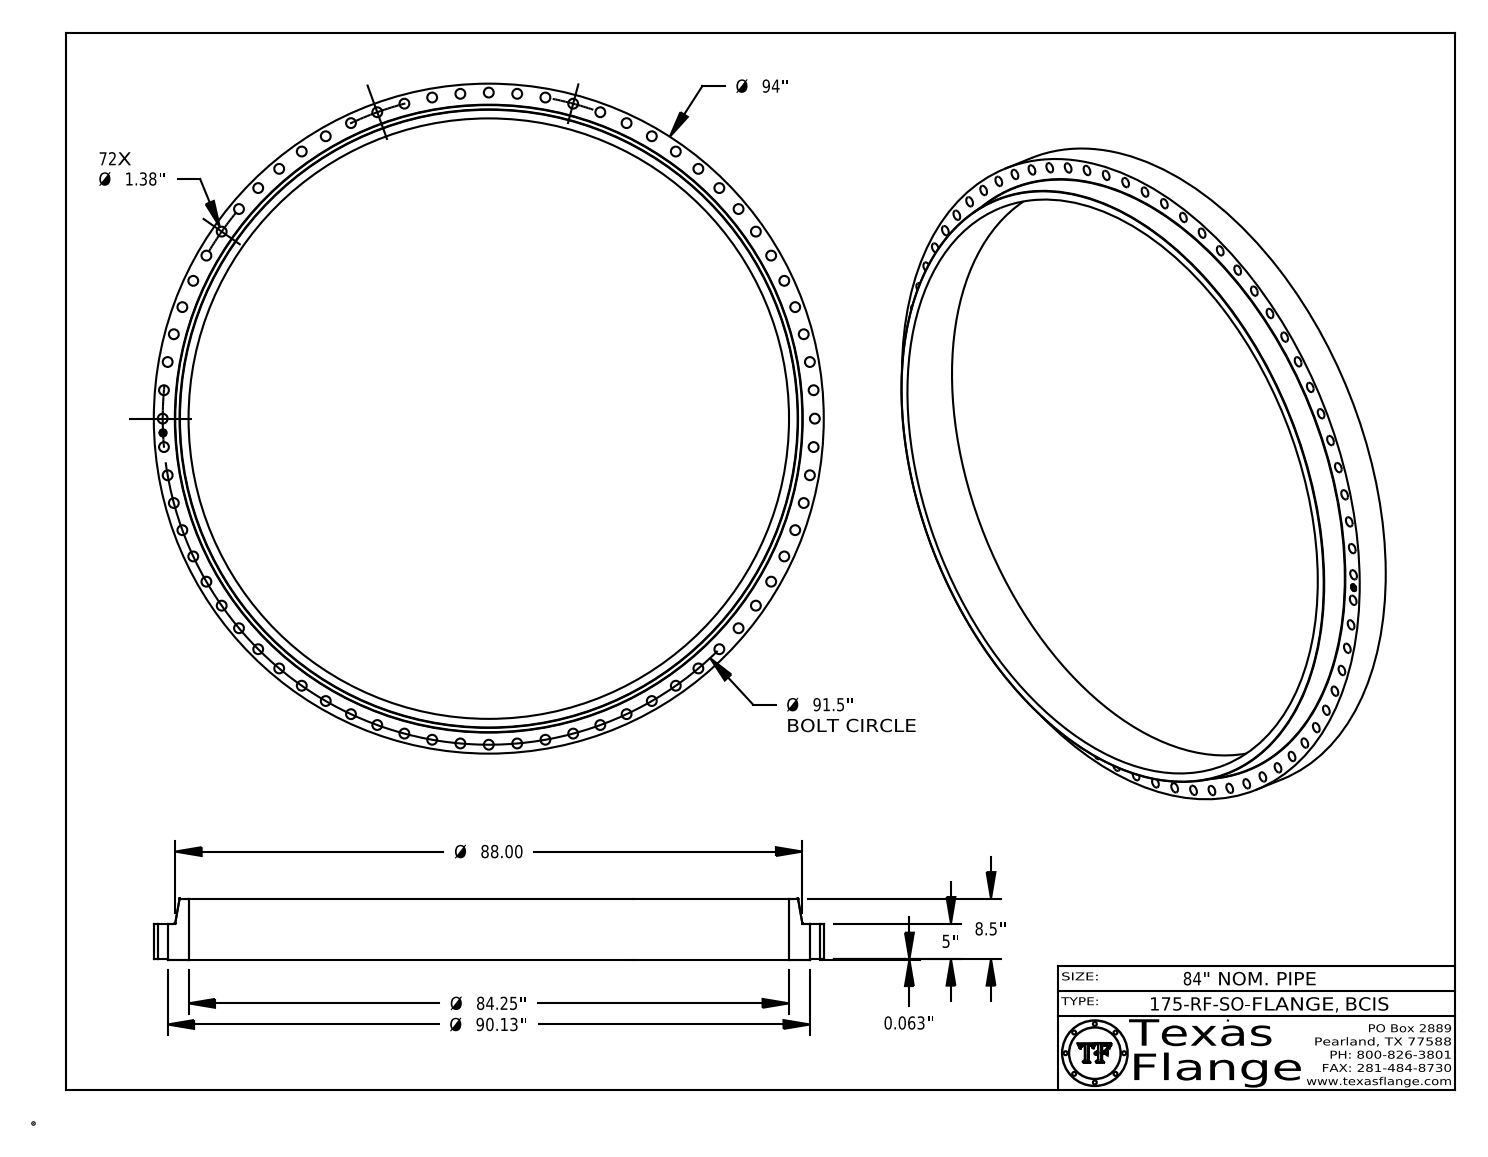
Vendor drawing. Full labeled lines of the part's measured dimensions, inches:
Part name (STEP PRODUCT): 175-RF-SO
STEP written by: CATIA V5 STEP AP214 (AUTOMOTIVE_DESIGN)
Units: inches
Bodies: 1 solid, 617 faces (369 planar, 242 cylindrical, 6 other)
Overall size (bounding box): 94 × 94 × 8.563
Volume: 7 815 in³ · Surface area: 8 633 in²
Round holes (diameter × count): ⌀1.38 ×72, ⌀1 ×1, ⌀84.25 ×1
Round bosses / shafts (diameter × count): ⌀0.061 ×8, ⌀94 ×1, ⌀90.13 ×1, ⌀0.788 ×1
Main face-to-face distances: 5.063, 0.063, 5, 8.563, 8.5, 3.5, 0.015, 5.048, 4.985, 3.515
Hole centre spacings: 45.75, 11.943, 3.991, 7.975, 19.804, 45.75, 15.889, 31.295
